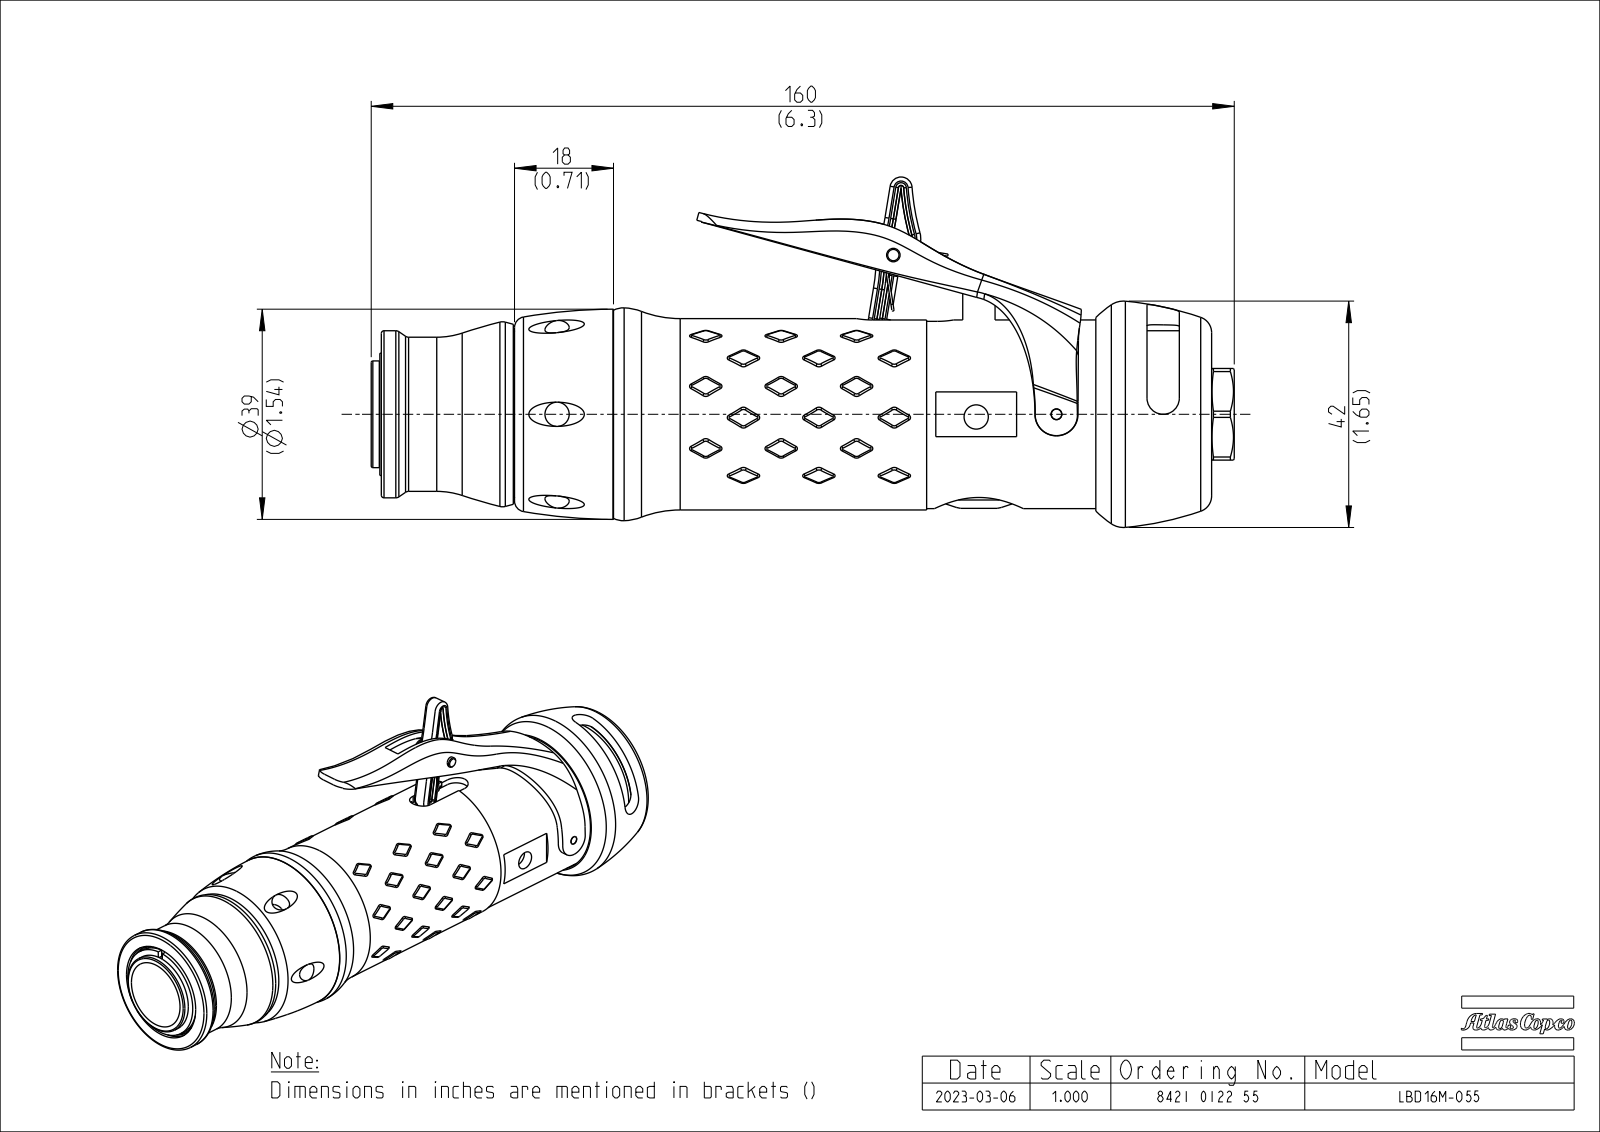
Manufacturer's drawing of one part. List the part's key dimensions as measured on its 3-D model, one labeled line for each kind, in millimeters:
Part name (STEP PRODUCT): EXT_COMP_SW0001
STEP written by: CREO PARAMETRIC BY PTC INC, 2020281 (CONFIG_CONTROL_DESIGN)
Units: millimetres
Bodies: 1 solid, 968 faces (286 planar, 165 cylindrical, 517 other)
Overall size (bounding box): 160.2 × 65 × 42
Volume: 153 100 mm³ · Surface area: 43 170 mm²
Round holes (diameter × count): ⌀4.5 ×4, ⌀3 ×2, ⌀2 ×1, ⌀2.7 ×1, ⌀3.4 ×1, ⌀6.8 ×1, ⌀8.5 ×1, ⌀11.8 ×1, ⌀16.5 ×1, ⌀19.2 ×1, ⌀35.3 ×1
Round bosses / shafts (diameter × count): ⌀35.5 ×1, ⌀35 ×1, ⌀33.4 ×1, ⌀32.7 ×1, ⌀32.6 ×1, ⌀32 ×1, ⌀31 ×1, ⌀28.6 ×1
Partial cylindrical surfaces — rounded edges, fillets, slot ends (radius × count): R0.5 ×16, R0.8 ×8, R3 ×7, R2.5 ×2, R4 ×2, R0.9 ×1, R9.5 ×1, R10 ×1
Main face-to-face distances: 16, 16.2, 154.1, 138.2, 137.9, 156, 140, 139.8, 1.9, 10
Hole centre spacings: 5.7, 11.4, 14.9, 33.8, 42.3, 69.1, 77.8, 92.7
